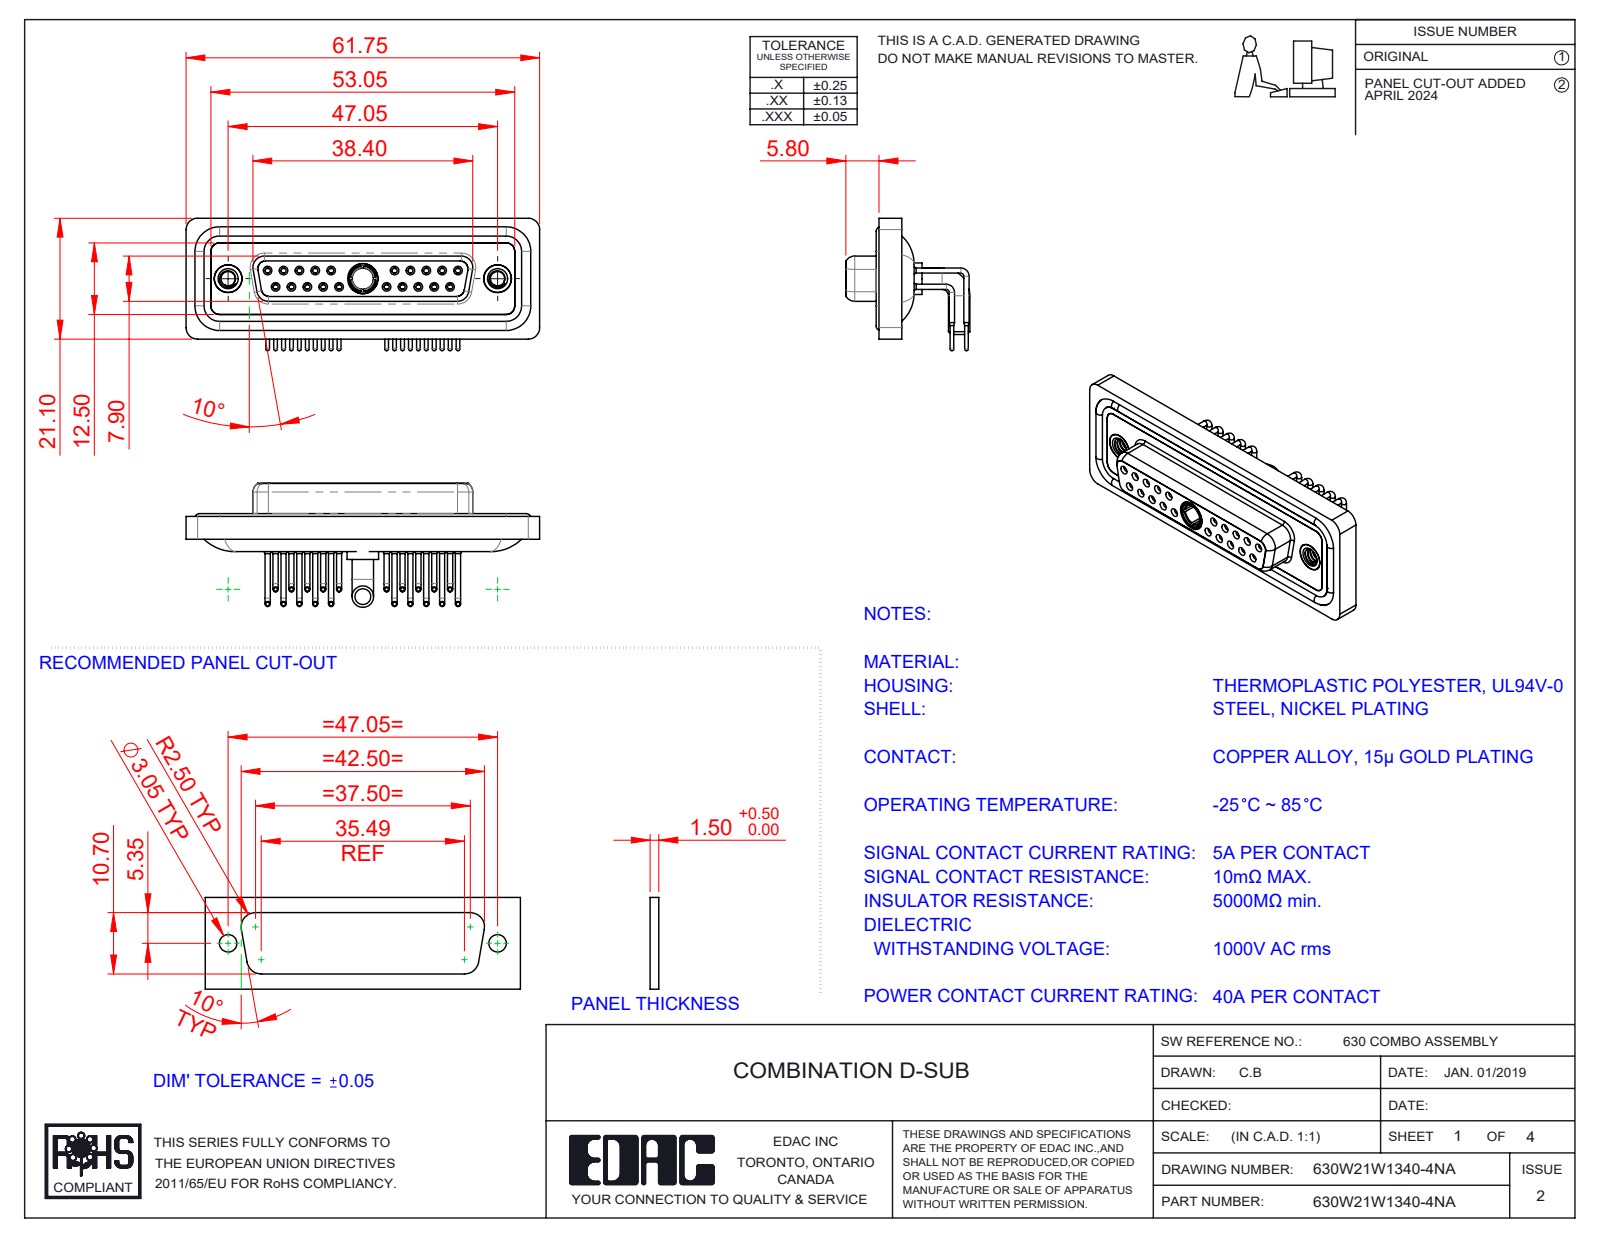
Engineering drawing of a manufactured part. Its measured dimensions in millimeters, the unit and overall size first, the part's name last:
Units: millimetres
Overall size (bounding box): 61.75 × 23.12 × 21.68
Round holes (diameter × count): ⌀0.9 ×20, ⌀1.1 ×20, ⌀1.5 ×20, ⌀2 ×20, ⌀1.6 ×10, ⌀1.7 ×10, ⌀4.85 ×3, ⌀2.5 ×2, ⌀4 ×2, ⌀4.05 ×2, ⌀5 ×2, ⌀3.7 ×1
Round bosses / shafts (diameter × count): ⌀0.9 ×20, ⌀0.65 ×20, ⌀1.6 ×14, ⌀4.95 ×2, ⌀4.8 ×2, ⌀3.75 ×2, ⌀5.5 ×1, ⌀5.2 ×1
Partial cylindrical surfaces — rounded edges, fillets, slot ends (radius × count): R1.5 ×18, R2 ×18, R1.35 ×8, R1.6 ×8, R0.25 ×4, R0.5 ×4, R0.6 ×4, R0.65 ×4
Main face-to-face distances: 0.4, 1.8, 4.1, 1.6, 1.1, 2.5, 3.1, 1.5, 9.8, 0.45
Hole centre spacings: 3.16, 2.77, 5.54, 8.31, 5.04, 19.39, 20.97, 22.16
Volume: 8 571 mm³ · Surface area: 14 827 mm²
Bodies: 29 solids, 1518 faces (434 planar, 671 cylindrical, 413 other)
Part name (STEP PRODUCT): 630W21W1340-4NA; 630Combo Shell Rear_25 Contacts; 630Combo Housing_21W1; 630Combo Shell Front_25 Contacts (+5 more)
STEP written by: SolidWorks 2023 (CONFIG_CONTROL_DESIGN)
